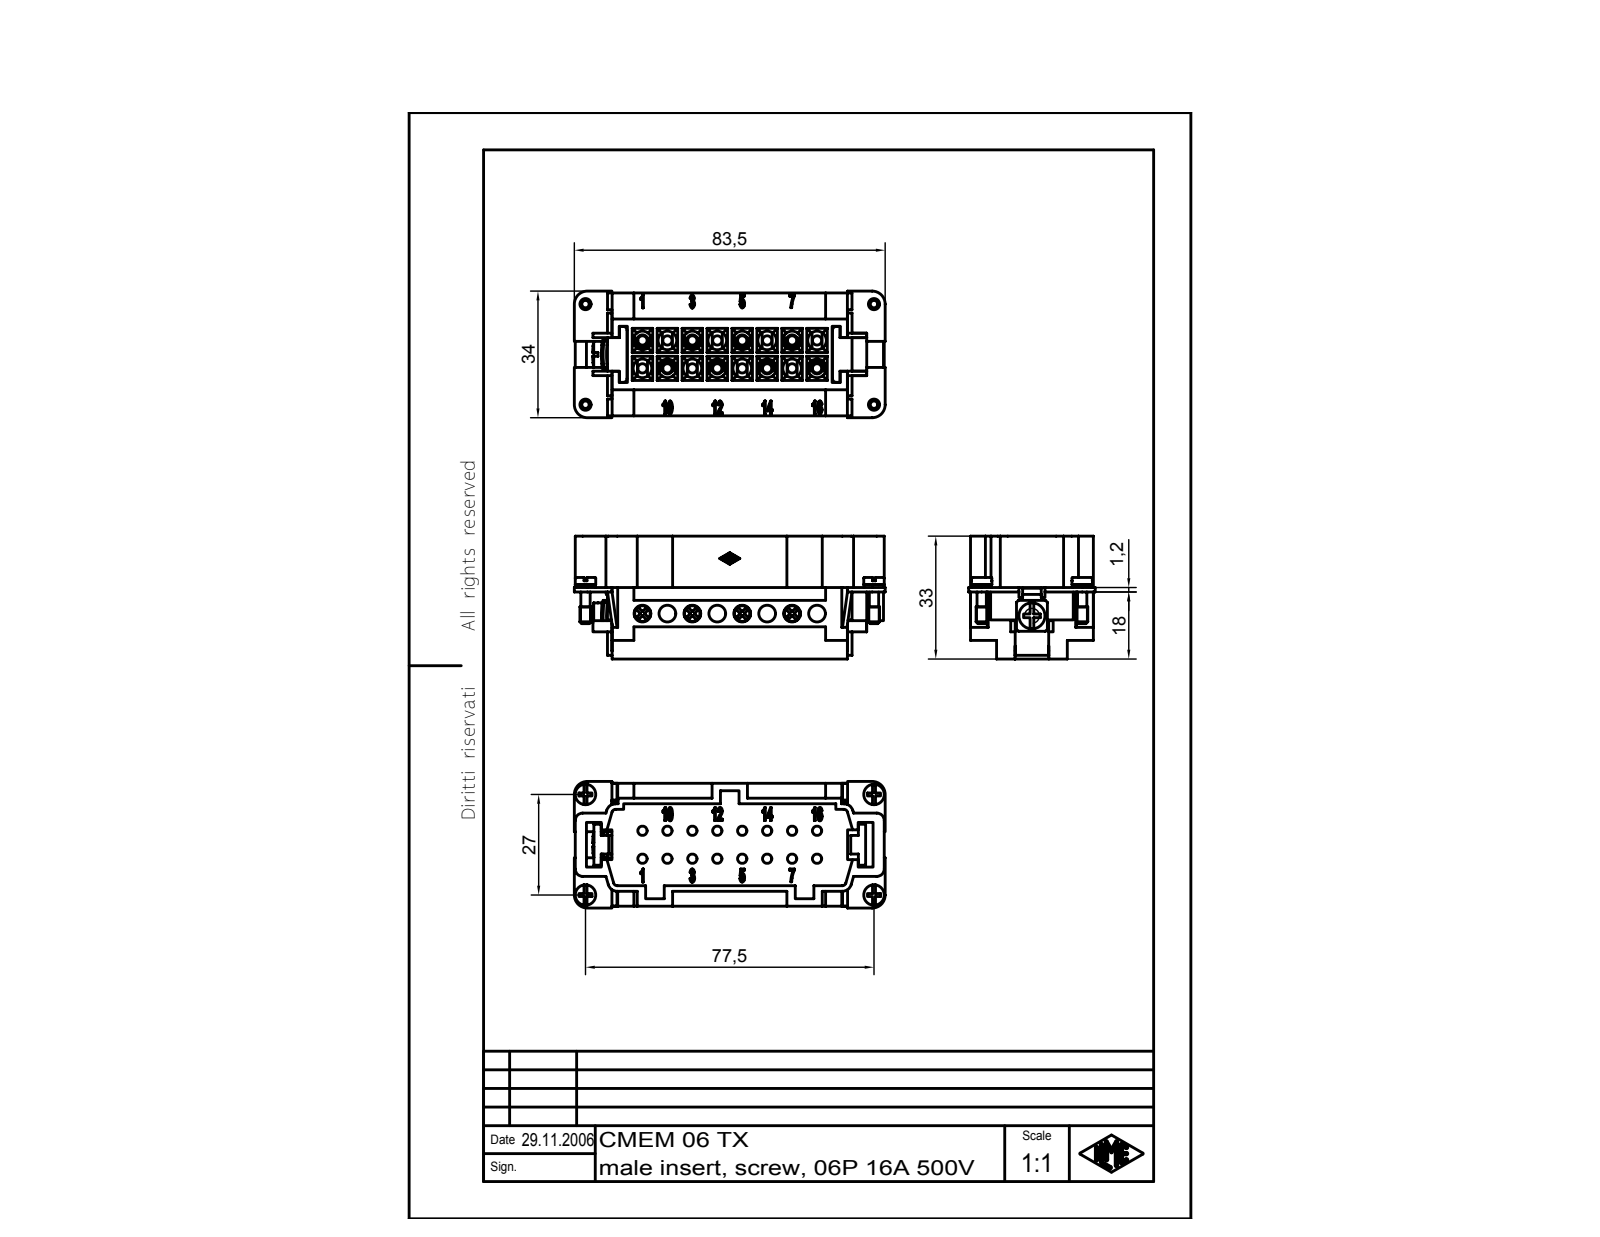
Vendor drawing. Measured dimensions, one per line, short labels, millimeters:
name: CMEM 06 TX
written by: Autodesk Inventor 7 (AUTOMOTIVE_DESIGN)
unit: mm
bodies: 9 solids, 1387 faces (692 planar, 229 cylindrical, 466 other)
size: 83.5 × 34 × 33
volume: 33 058 mm³; area: 29 940 mm²
holes: 8× ⌀2.5, 8× ⌀3, 8× ⌀4.5, 8× ⌀5, 2× ⌀2.55
bosses: 8× ⌀4.2, 6× ⌀2.5, 2× ⌀5.5, 2× ⌀5.3, 2× ⌀3, 1× ⌀7
rounds: 14× R0.1, 8× R2.1, 6× R1, 6× R2, 4× R2.5, 2× R3.5, 1× R1.62, 1× R5.5
face distances: 1.5, 22, 3, 20.5, 4, 5.5, 23.5, 29, 7, 1
hole spacings: 6.7, 13.4, 20.1, 10.06, 15.36, 26.8, 21.45, 33.5
